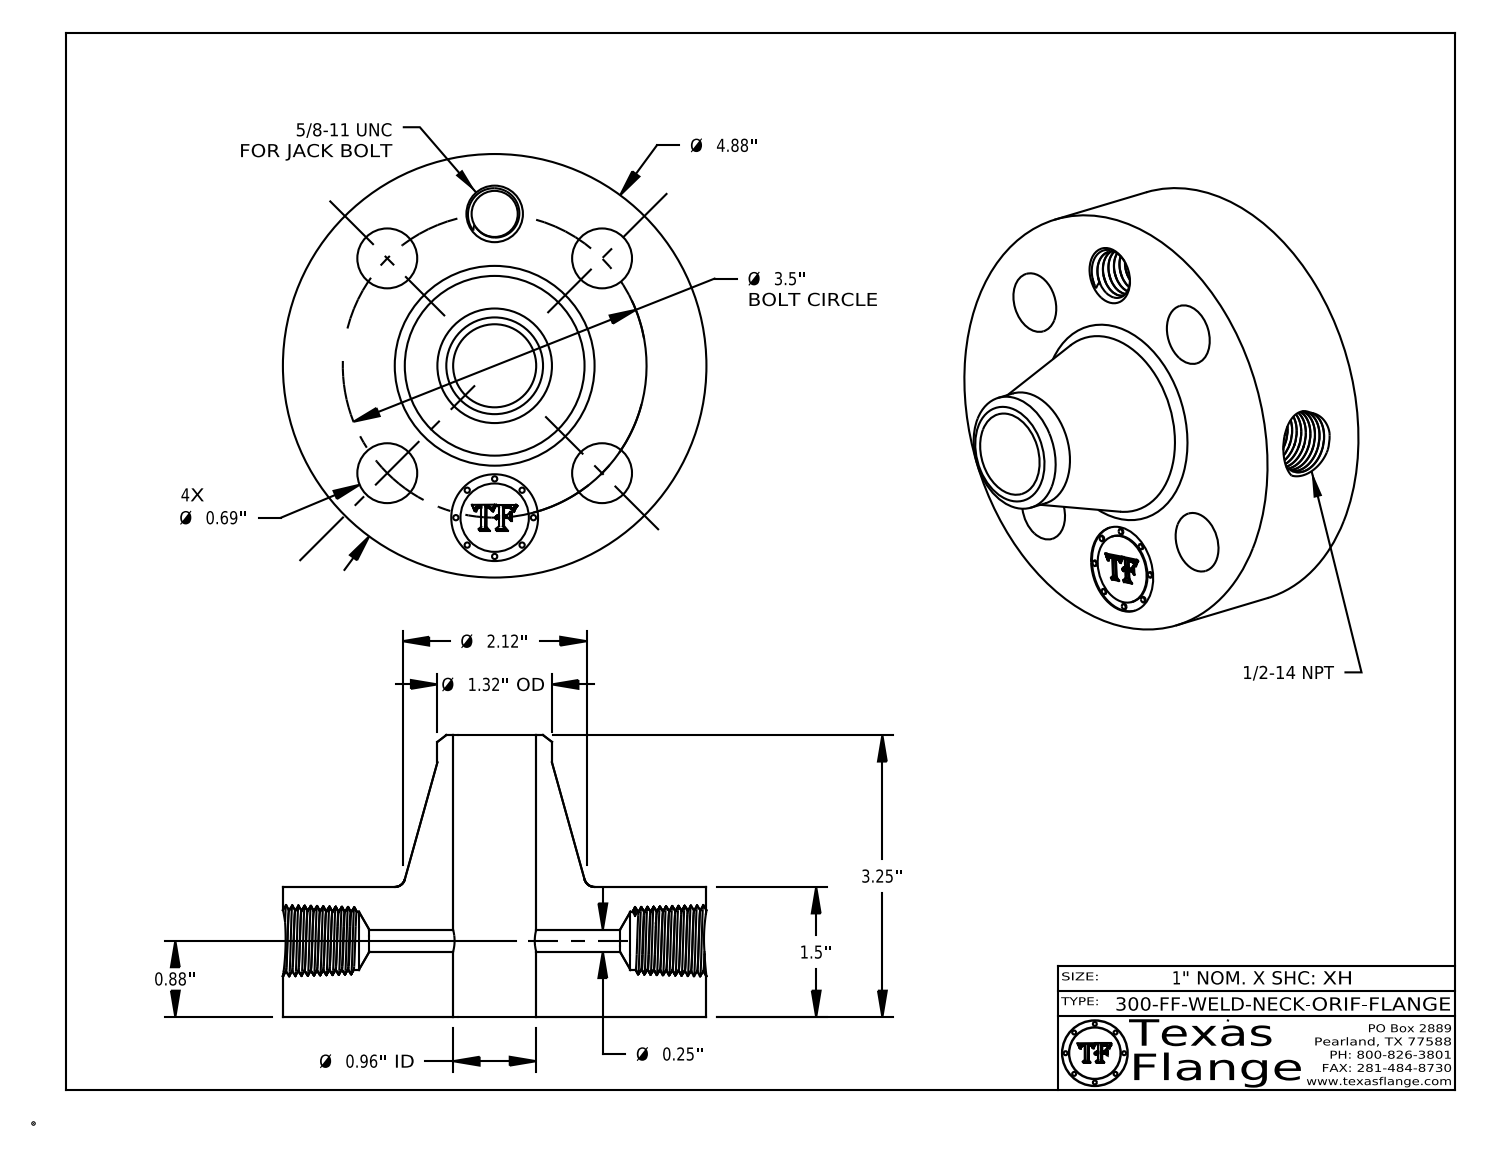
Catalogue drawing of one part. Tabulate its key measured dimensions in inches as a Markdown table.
| quantity | value |
| --- | --- |
| part name | 300-FF-WELD-NECK |
| STEP written by | CATIA V5 STEP AP214 (AUTOMOTIVE_DESIGN) |
| units | inches |
| bodies | 1 solid, 761 faces (368 planar, 85 cylindrical, 308 other) |
| overall size | 4.88 × 4.88 × 3.25 |
| volume | 26.02 in³ |
| surface area | 97.4 in² |
| round holes (diameter × count) | 0.69 × 4, 0.25 × 1, 0.531 × 1, 0.672 × 1, 0.957 × 1, 1 × 1 |
| round bosses / shafts (diameter × count) | 0.061 × 8, 4.88 × 1, 1.32 × 1, 0.788 × 1 |
| main face-to-face distances | 1.5, 1.485, 0.015, 3.25, 1.765, 1.75, 0.298, 0.293, 0.054, 0.248 |
| hole center spacings | 1.75, 1.339, 2.475, 3.233, 3.5 |
